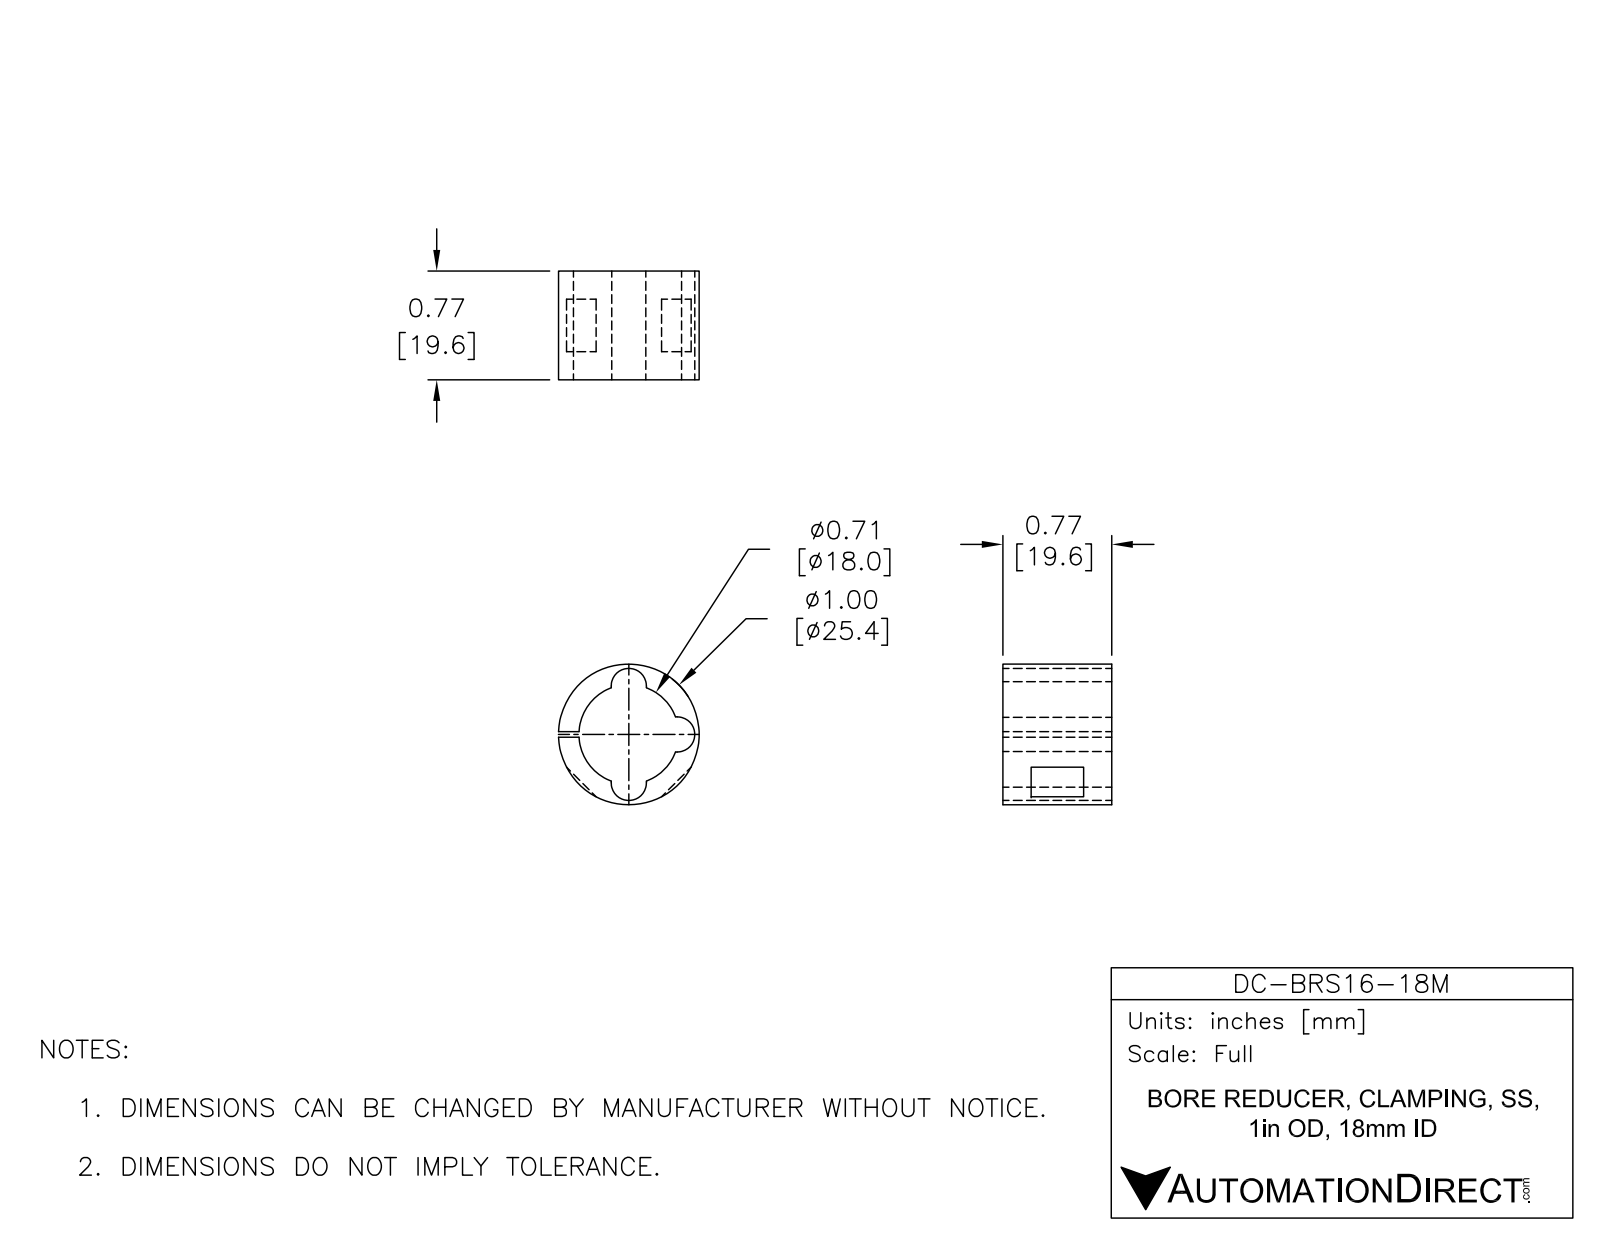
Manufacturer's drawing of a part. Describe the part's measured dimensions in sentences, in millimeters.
The part is named "DC-BRS16-18M". Its 3-D file was written by "SolidWorks 2015 (AUTOMOTIVE_DESIGN)". It is 1 solid with 27 faces: 16 planar, 11 cylindrical and 0 other. Overall it measures 25.4 by 25.39 by 19.63 millimeters. Its volume is 3 918 cubic millimeters and its surface area 3 439 square millimeters. Round bosses or shafts: 1 of diameter 25.4. Partial cylindrical surfaces (rounded edges, fillets, slot ends): 3 of radius 3.17, 1 of radius 9. The main face-to-face distances are 19.64, 1.02, 6.34, 2.66, 3.68, 5.08, 14.56, 9.48.
